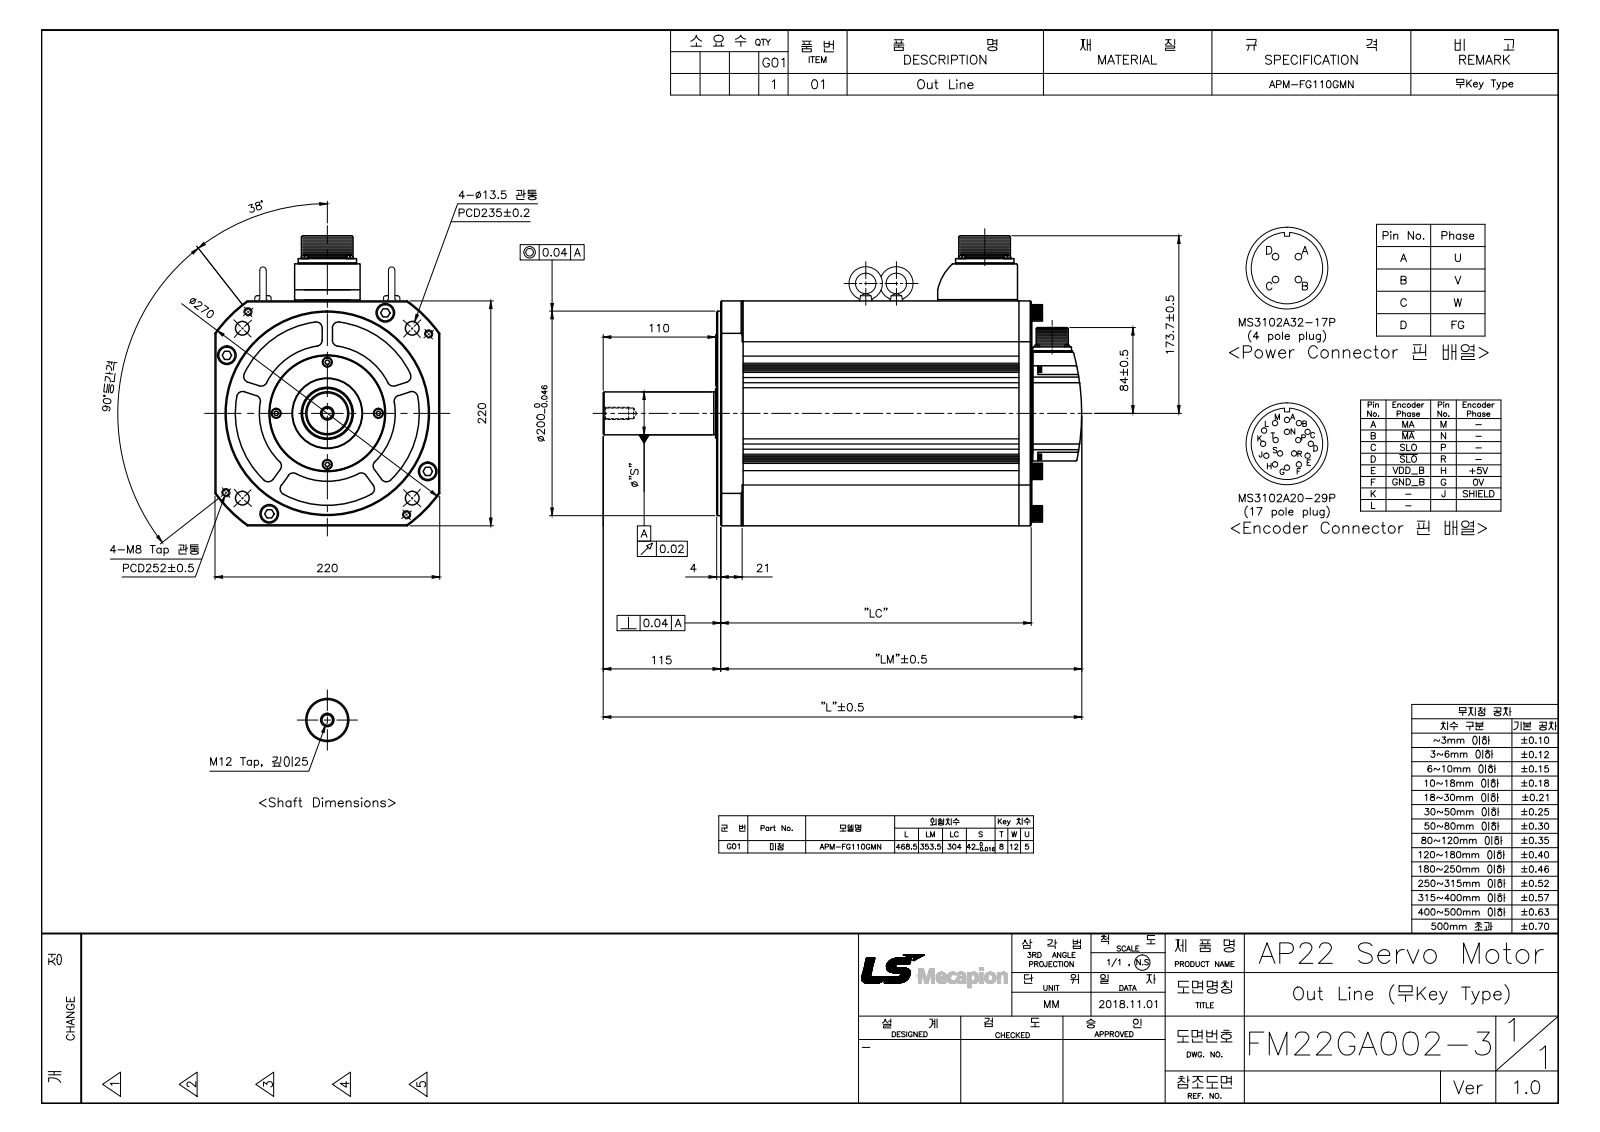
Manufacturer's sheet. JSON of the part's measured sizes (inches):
{"part_name": "FM22GA002-3_Out Line(APM-FG110G_N)", "step_written_by": "SolidWorks 2011 (AUTOMOTIVE_DESIGN)", "units": "inches", "bodies": {"solids": 56, "faces": 2109, "planar": 709, "cylindrical": 834, "other": 566}, "overall_size": [18.445, 11.169, 8.661], "volume_in3": 817.7, "surface_area_in2": 1273, "round_holes": [[0.098, 8], [0.118, 8], [0.12, 6], [0.315, 6], [0.13, 4], [0.138, 4], [0.142, 4], [0.146, 4], [0.157, 4], [0.165, 4], [0.189, 4], [0.197, 4]], "round_bosses_or_shafts": [[0.063, 17], [0.63, 4], [0.335, 4], [0.276, 4], [0.236, 4], [0.217, 4], [0.213, 4], [7.913, 1]], "partial_cylinders_radius": [[0.039, 116], [0.236, 24], [0.079, 17], [0.197, 16], [0.157, 14], [0.177, 12], [0.02, 8], [0.012, 2]], "face_to_face_distances": [10.63, 1.575, 8.661, 7.087, 0.827, 0.472, 0.551, 5.512, 0.039, 2.756], "hole_center_spacings": [3.521, 6.177, 0.674, 0.819, 1.072, 1.157, 1.197, 1.239]}
